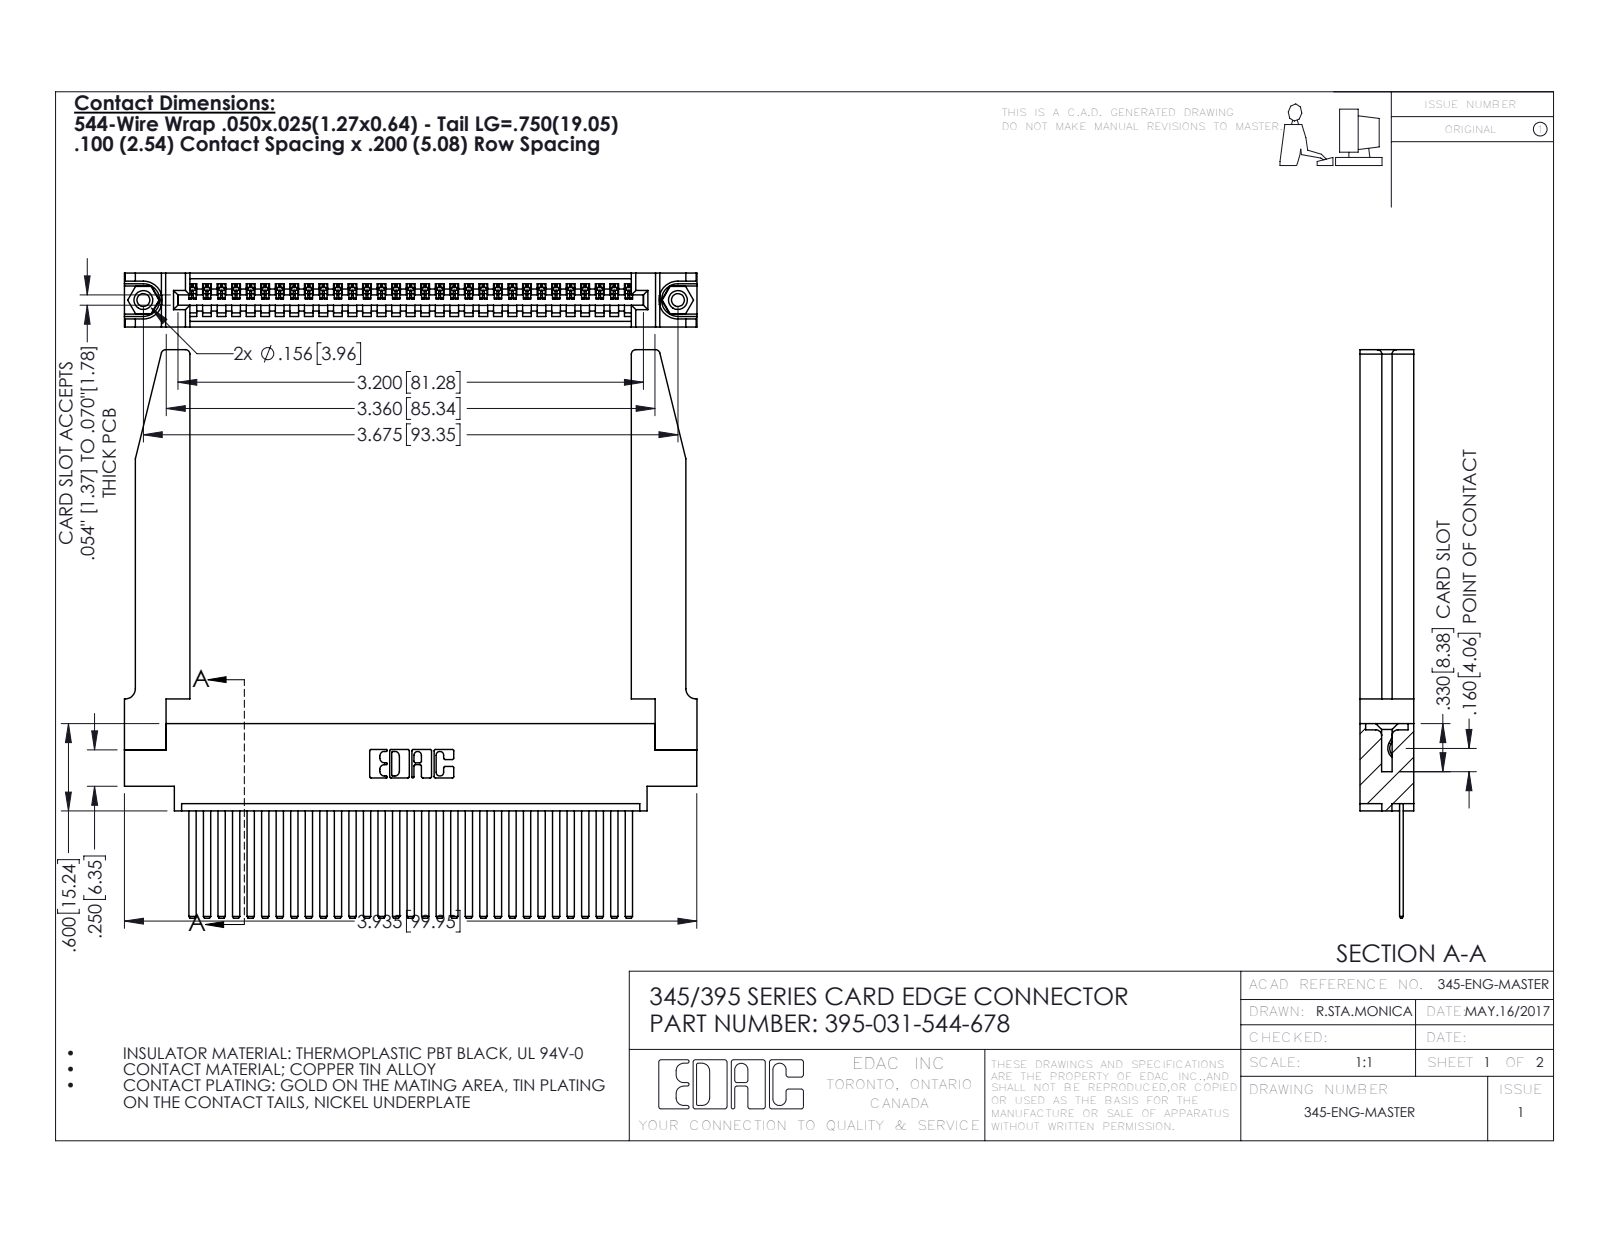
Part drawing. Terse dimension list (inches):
name: 345 Part_0.170 Offset - 0.156 Dia-TH; 345-220-078_345-220-078; 395-031-544-678; 345-292-001_345-293-144 (+1 more)
written by: SolidWorks 2016 (CONFIG_CONTROL_DESIGN)
unit: in
bodies: 36 solids, 1976 faces (1342 planar, 582 cylindrical, 52 other)
size: 3.936 × 3.907 × 0.37
volume: 1.063 in³; area: 32.13 in²
holes: 2× ⌀0.089, 2× ⌀0.125, 2× ⌀0.156, 1× ⌀0.064
bosses: 2× ⌀0.155
rounds: 62× R0.006, 22× R0.01, 8× R0.03, 6× R0.007, 6× R0.031, 3× R0.026, 2× R0.031, 2× R0.04
face distances: 0.37, 0.072, 0.298, 0.098, 0.272, 0.025, 0.2, 0.15, 0.148, 0.225
hole spacings: 0.27, 3.44, 3.675
